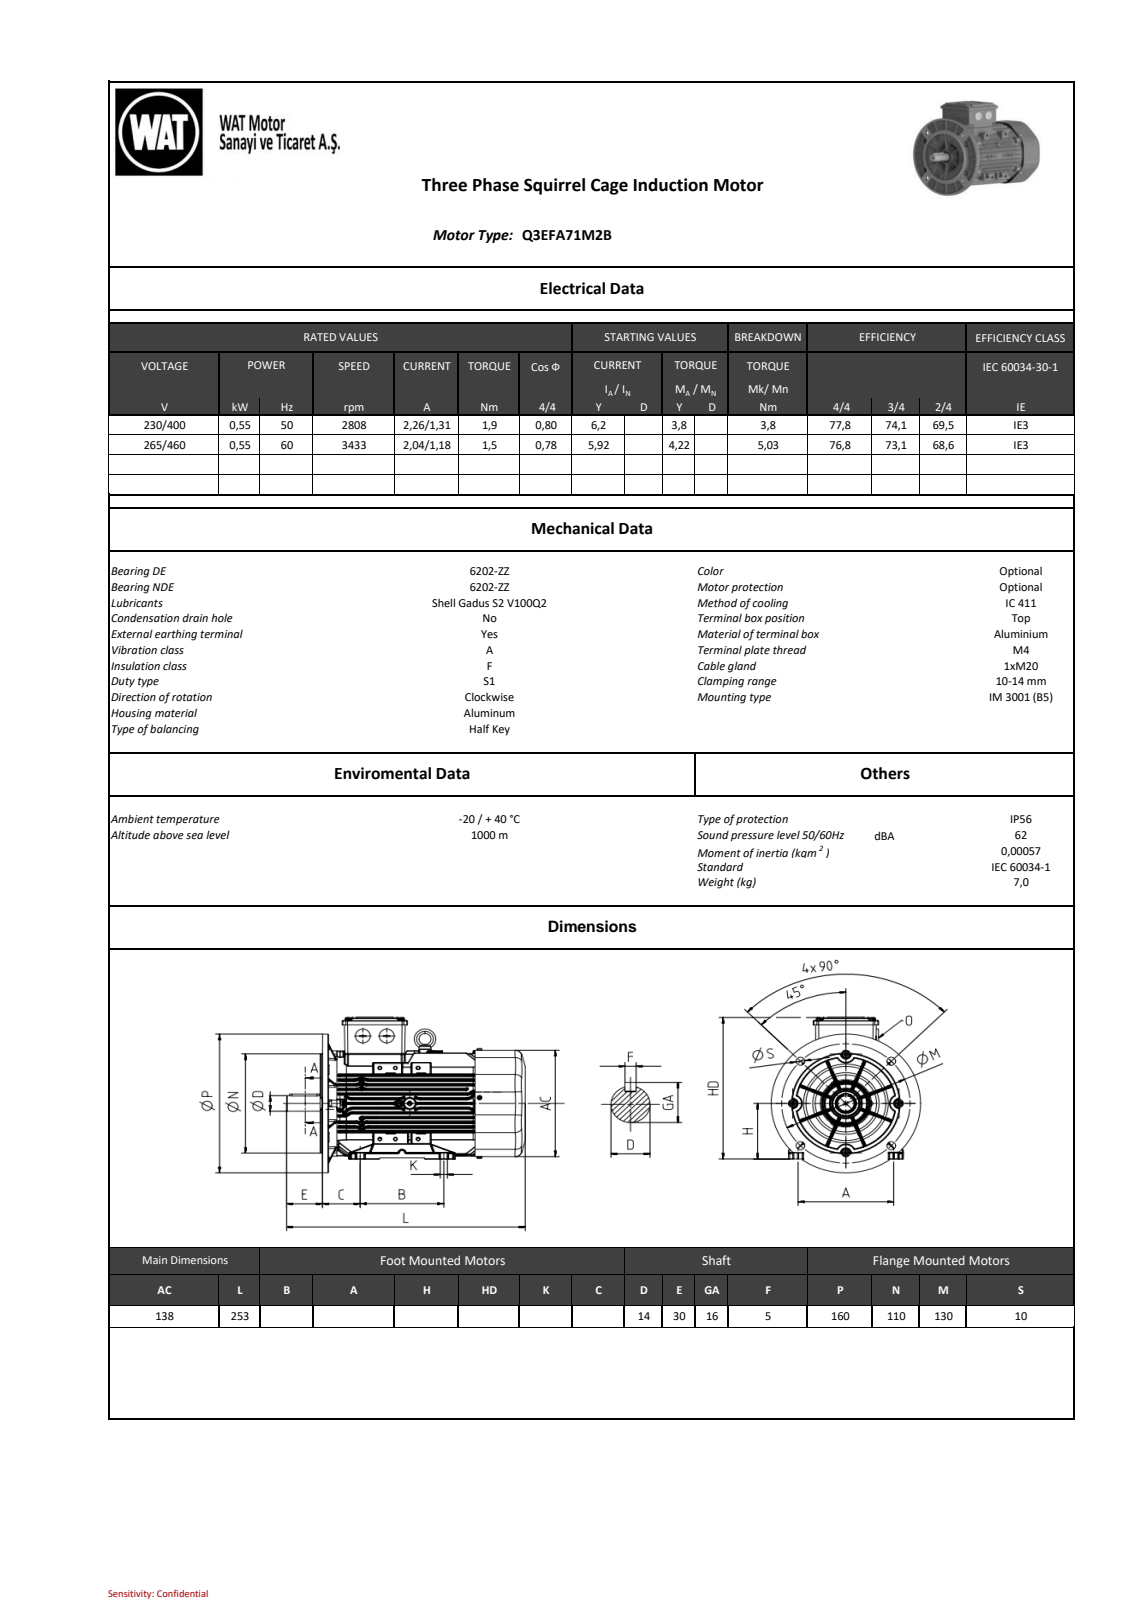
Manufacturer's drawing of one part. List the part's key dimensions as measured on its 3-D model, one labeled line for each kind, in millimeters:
Part name (STEP PRODUCT): 001_objects
STEP written by: SIEMENS PLM Software NX2206.8101 (AUTOMOTIVE_DESIGN)
Units: millimetres
Bodies: 0 solids, 3055 faces (1378 planar, 759 cylindrical, 918 other)
Overall size (bounding box): 252 × 187.11 × 160
Round holes (diameter × count): ⌀3.3 ×13, ⌀3.65 ×8, ⌀2.5 ×6, ⌀5 ×5, ⌀4.5 ×4, ⌀4.65 ×4, ⌀4.8 ×4, ⌀10 ×4, ⌀3 ×3, ⌀3.7 ×3, ⌀4.6 ×2, ⌀6 ×1
Round bosses / shafts (diameter × count): ⌀8 ×8, ⌀4 ×8, ⌀160 ×1, ⌀138 ×1, ⌀136 ×1, ⌀110 ×1, ⌀61 ×1, ⌀26 ×1
Partial cylindrical surfaces — rounded edges, fillets, slot ends (radius × count): R1 ×103, R0.5 ×48, R1.2 ×36, R2 ×34, R1.5 ×28, R10 ×24, R4 ×23, R0.75 ×18
Main face-to-face distances: 2, 3, 5, 185.5, 35, 83, 1, 177.2, 38.5, 182.2
Hole centre spacings: 61.39, 89.74, 55, 36.59, 65, 67.18, 67.2, 60
